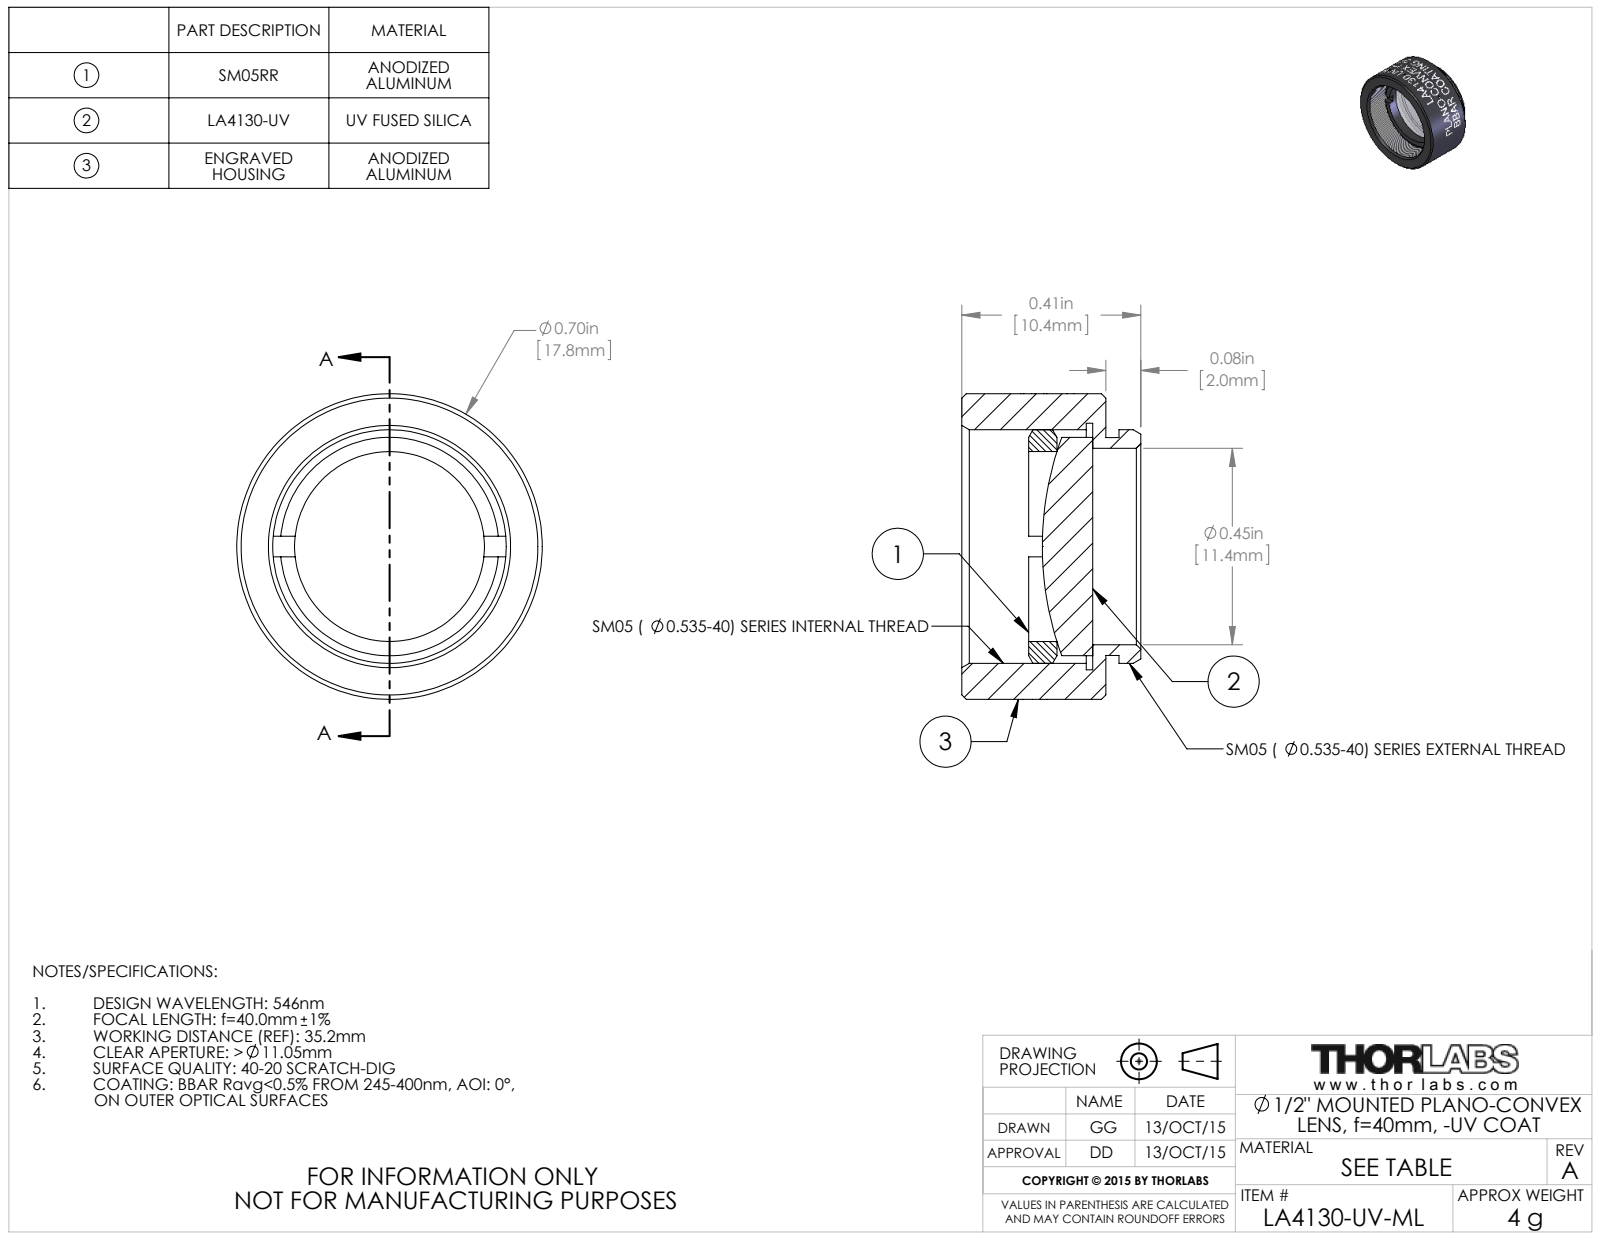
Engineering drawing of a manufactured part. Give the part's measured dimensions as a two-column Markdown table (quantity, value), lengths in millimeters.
| quantity | value |
| --- | --- |
| part name | TTN039162-E0W |
| STEP written by | SolidWorks 2014 (CONFIG_CONTROL_DESIGN) |
| units | millimeters |
| bodies | 3 solids, 142 faces (16 planar, 109 cylindrical, 17 other) |
| overall size | 17.78 × 17.78 × 10.41 |
| volume | 1 328 mm³ |
| surface area | 1 844 mm² |
| round holes (diameter × count) | 11.05 × 1, 11.43 × 1, 13.59 × 1, 14.35 × 1 |
| round bosses / shafts (diameter × count) | 17.78 × 1, 13.59 × 1, 12.7 × 1, 12.67 × 1 |
| main face-to-face distances | 0.76, 8.38, 7.62, 2.85, 2.09, 5.53, 4.5, 3.74, 1.65, 3.88 |
